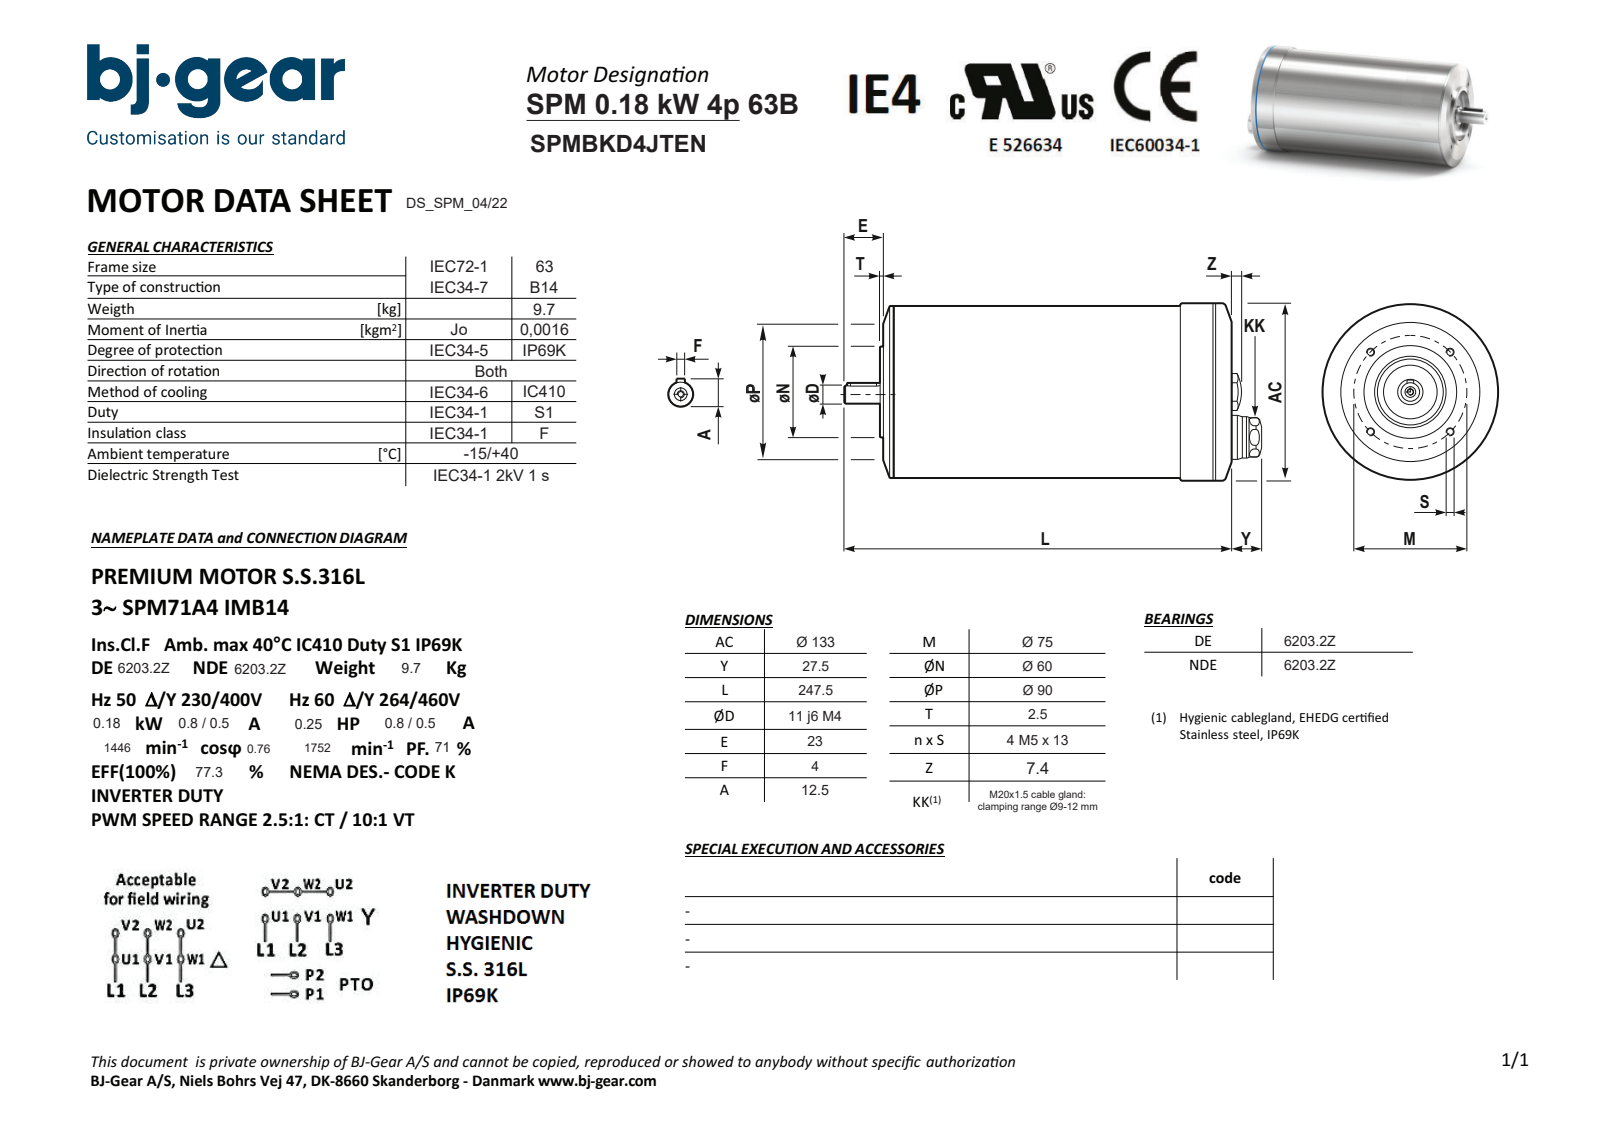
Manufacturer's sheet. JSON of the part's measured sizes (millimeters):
{"part_name": "SPMBKD4JTENN4KSA1-N---NNN", "step_written_by": "Solid Edge (AUTOMOTIVE_DESIGN)", "units": "millimeters", "bodies": {"solids": 1, "faces": 87, "planar": 30, "cylindrical": 32, "other": 25}, "overall_size": [275, 133, 133], "volume_mm3": 2939000, "surface_area_mm2": 120931, "round_holes": [[4.13, 4], [3.24, 1], [4.3, 1], [7, 1], [13.4, 1], [52, 1]], "round_bosses_or_shafts": [[133, 1], [132.98, 1], [129, 1], [128.98, 1], [60, 1], [20, 1], [17, 1], [11, 1]], "partial_cylinders_radius": [[2, 2], [12.8, 1]], "face_to_face_distances": [224.5, 219, 5.5, 2.5, 8, 227, 24, 12, 231, 236.5], "hole_center_spacings": [37.5, 53.04, 27.55, 66.08, 75.01, 34]}
